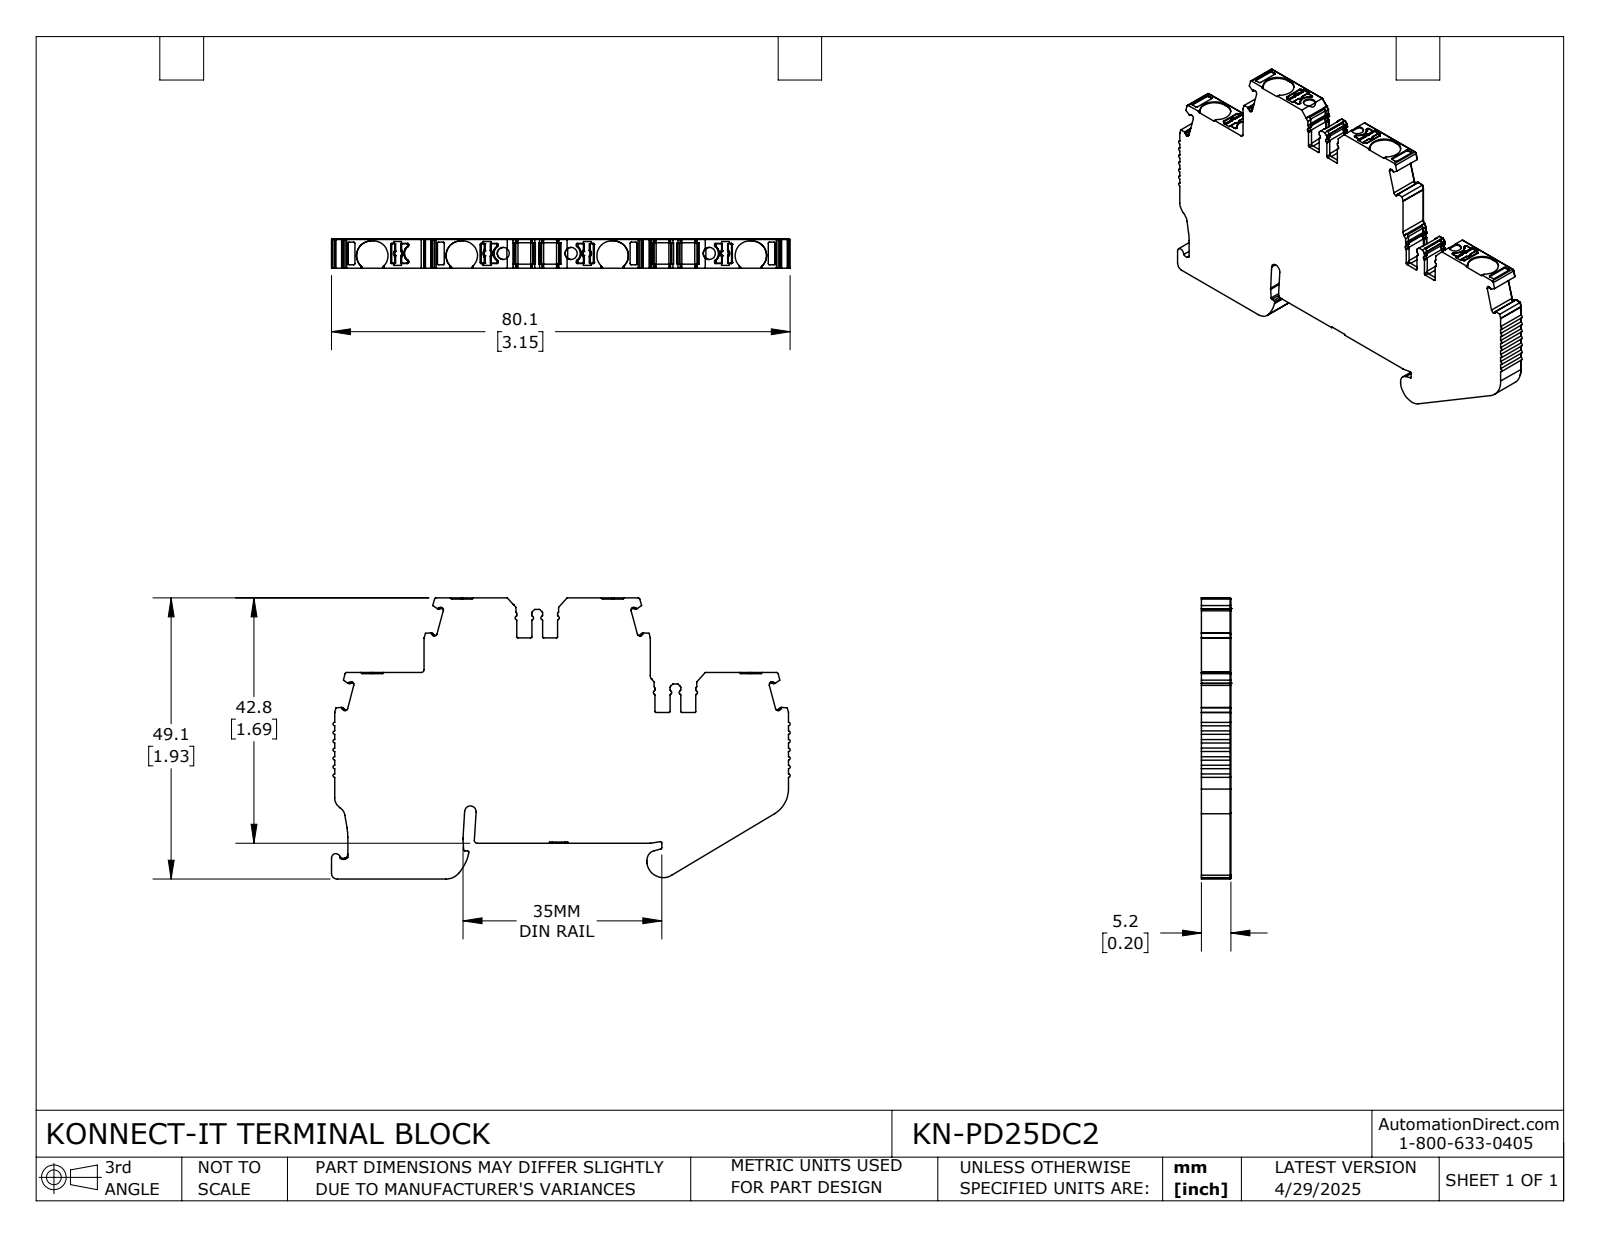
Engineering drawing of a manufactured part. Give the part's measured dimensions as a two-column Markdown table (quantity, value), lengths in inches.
| quantity | value |
| --- | --- |
| part name | KN-PD25DC2 |
| STEP written by | SolidWorks 2024 (CONFIG_CONTROL_DESIGN) |
| units | inches |
| bodies | 1 solid, 977 faces (472 planar, 438 cylindrical, 67 other) |
| overall size | 3.153 × 1.933 × 0.203 |
| volume | 0.889 in³ |
| surface area | 11.63 in² |
| round holes (diameter × count) | 0.083 × 3 |
| partial cylindrical surfaces (radius × count) | 0.008 × 100, 0.012 × 57, 0.004 × 41, 0.02 × 21, 0.016 × 17, 0.006 × 16, 0.024 × 9, 0.006 × 8 |
| main face-to-face distances | 0.203, 0.512, 0.246, 1.678, 1.166, 1.924, 0.079, 1.412, 0.504, 0.95 |
| hole center spacings | 0.466, 0.95, 1.417 |
